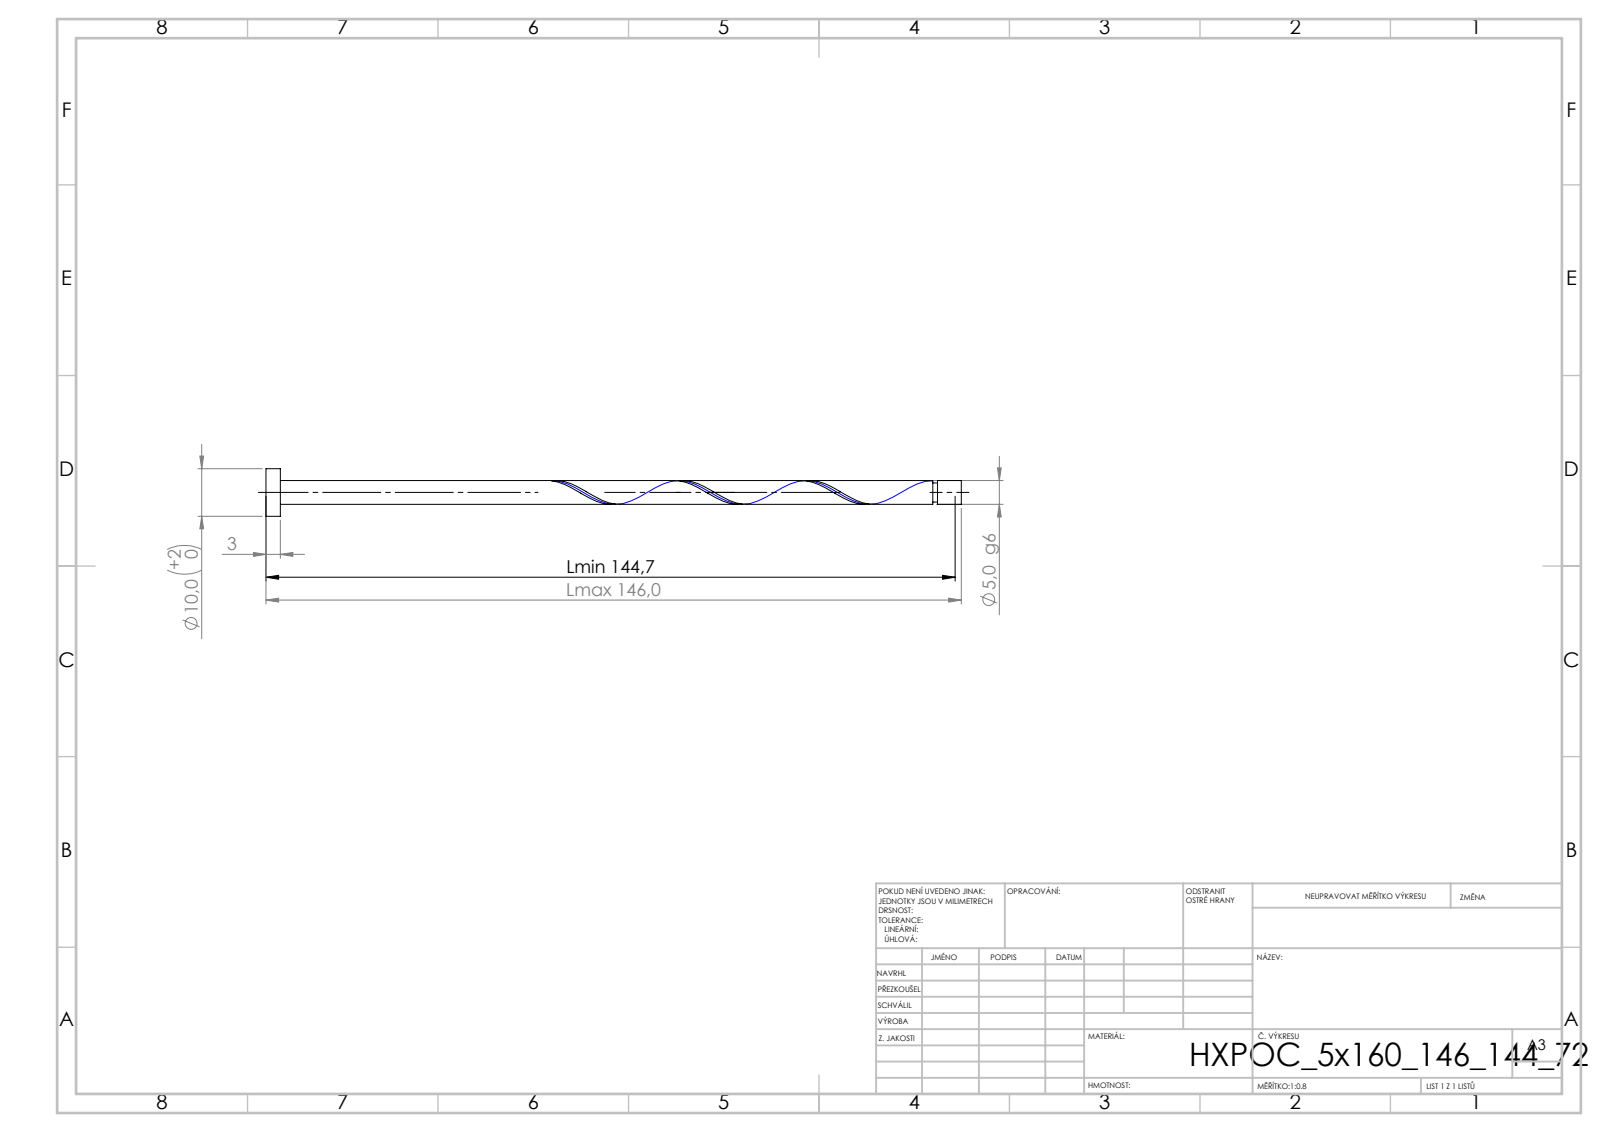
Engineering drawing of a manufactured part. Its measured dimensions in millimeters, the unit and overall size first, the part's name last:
Units: millimetres
Overall size (bounding box): 146 × 10 × 10
Round bosses / shafts (diameter × count): ⌀10 ×1, ⌀5 ×1, ⌀4 ×1
Main face-to-face distances: 3, 146, 143, 141.02, 138.02, 4.98, 140.02, 137.02, 1, 5.98
Volume: 3 006 mm³ · Surface area: 2 555 mm²
Bodies: 1 solid, 21 faces (6 planar, 14 cylindrical, 1 other)
STEP written by: SolidWorks 2019 (CONFIG_CONTROL_DESIGN)
